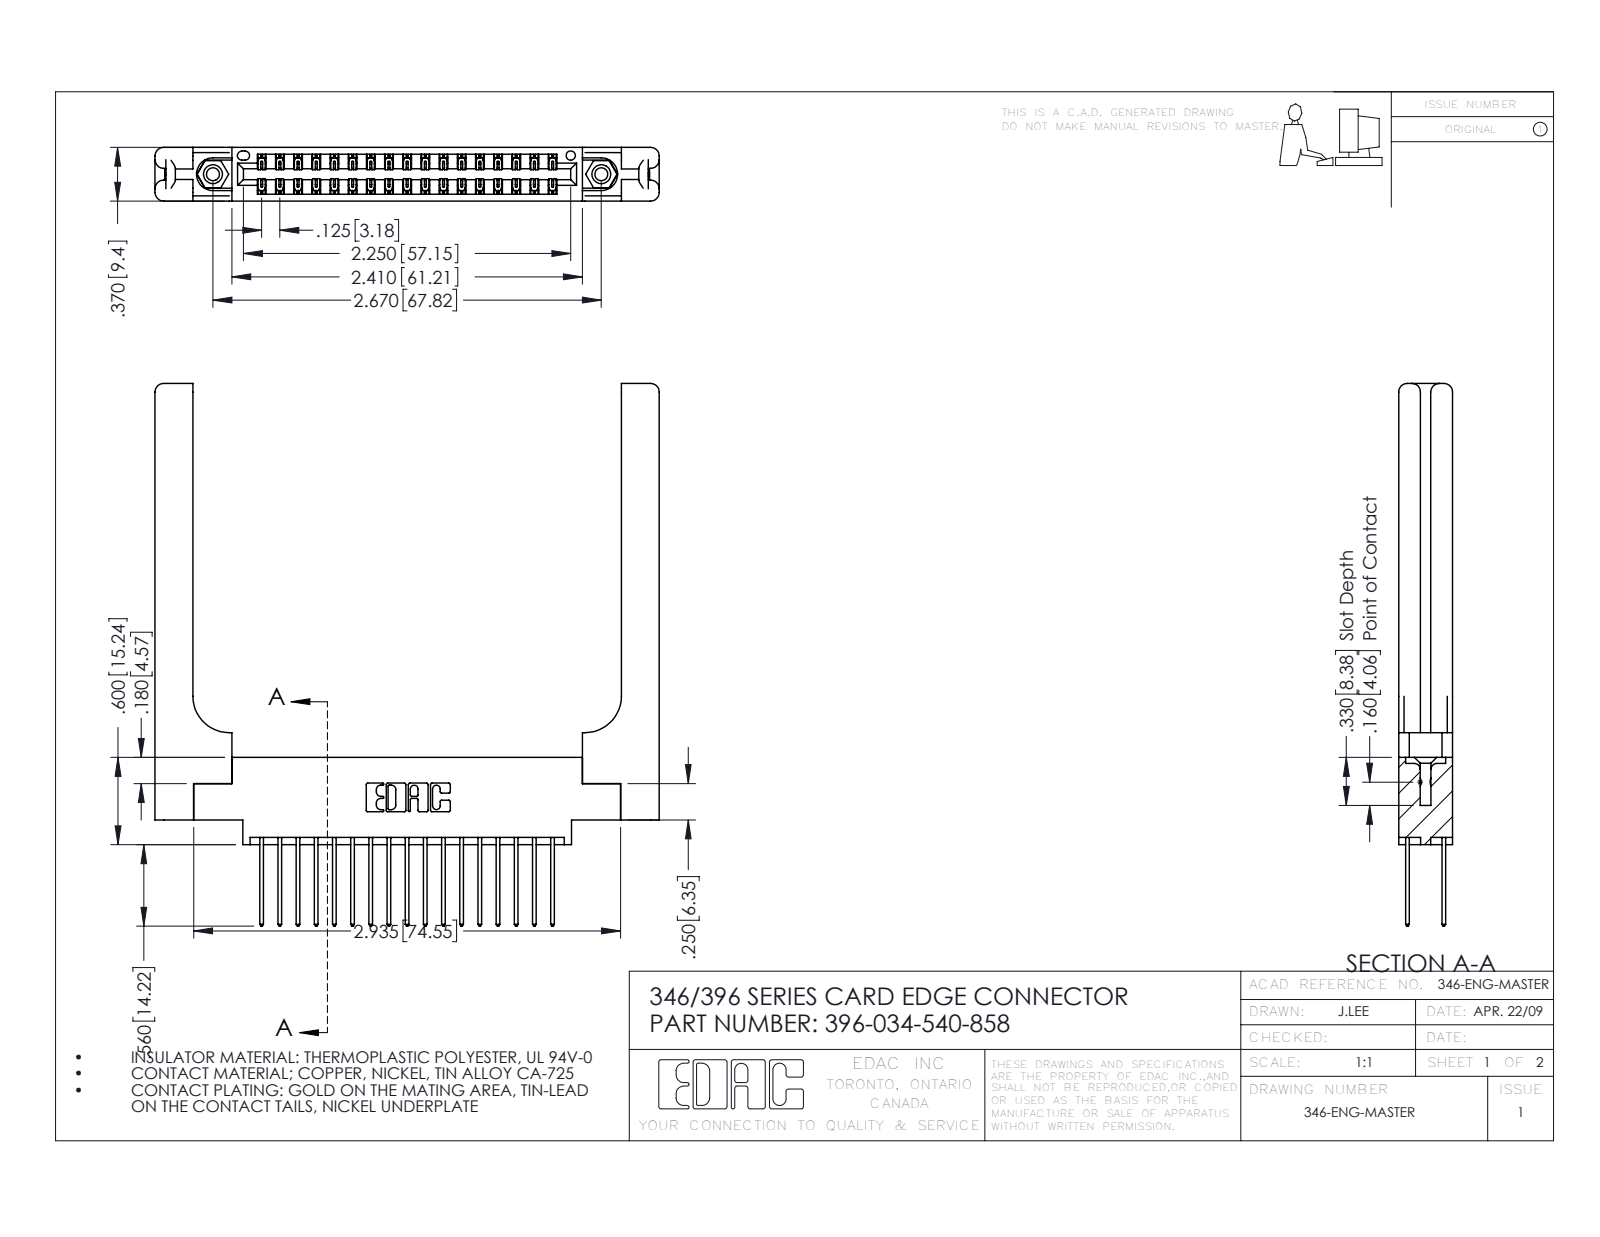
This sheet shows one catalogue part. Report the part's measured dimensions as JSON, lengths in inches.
{"part_name": "396-034-540-858; 346 Part_0.170 Offset - 0.156 Dia-TH; 345-250-001_345-250-001-102; 346-220-058_345-220-058 (+1 more)", "step_written_by": "SolidWorks 2016 (CONFIG_CONTROL_DESIGN)", "units": "inches", "bodies": {"solids": 39, "faces": 2150, "planar": 1418, "cylindrical": 672, "other": 60}, "overall_size": [3.73, 3.466, 0.37], "volume_in3": 0.968, "surface_area_in2": 26.14, "round_holes": [[0.089, 2], [0.125, 2], [0.156, 2], [0.064, 1]], "round_bosses_or_shafts": [[0.155, 2]], "partial_cylinders_radius": [[0.006, 51], [0.01, 34], [0.01, 22], [0.06, 16], [0.007, 6], [0.031, 6], [0.026, 3], [0.014, 2]], "face_to_face_distances": [0.37, 0.072, 0.048, 0.322, 0.15, 0.148, 0.25, 0.025, 0.298, 0.077], "hole_center_spacings": [0.246, 2.463, 2.67]}
